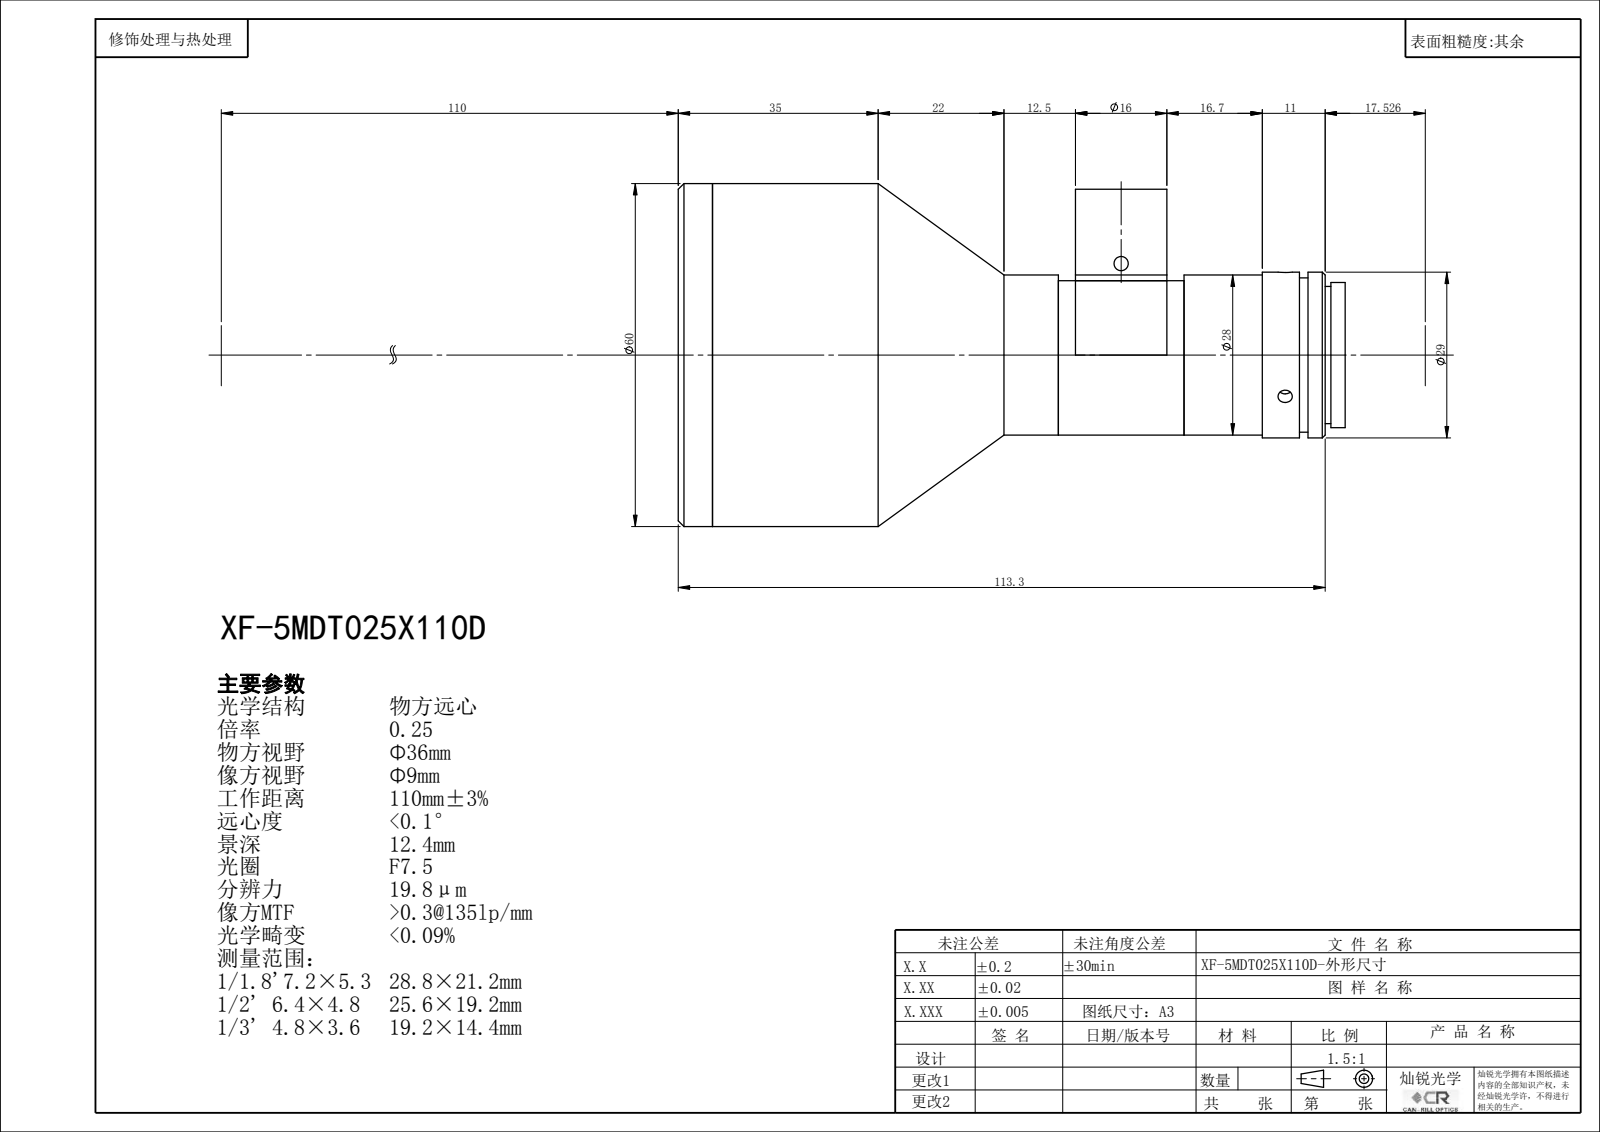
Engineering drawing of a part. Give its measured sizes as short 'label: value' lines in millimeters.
name: XF-5MDT0.25X110D
written by: SolidWorks 2014 (CONFIG_CONTROL_DESIGN)
unit: mm
bodies: 0 solids, 110 faces (37 planar, 65 cylindrical, 8 other)
size: 116.75 × 60 × 60
holes: 8× ⌀2.5, 4× ⌀1.6, 1× ⌀13, 1× ⌀14, 1× ⌀21.4, 1× ⌀46, 1× ⌀49.4, 1× ⌀54
bosses: 1× ⌀60, 1× ⌀29, 1× ⌀28, 1× ⌀27, 1× ⌀25.4, 1× ⌀24, 1× ⌀16
face distances: 6, 66.54, 60.54, 1, 44.71, 3, 2.38, 3.62, 64.16, 111.25
hole spacings: 11.51, 13, 19, 23.02, 24.16, 36.47, 28.71
